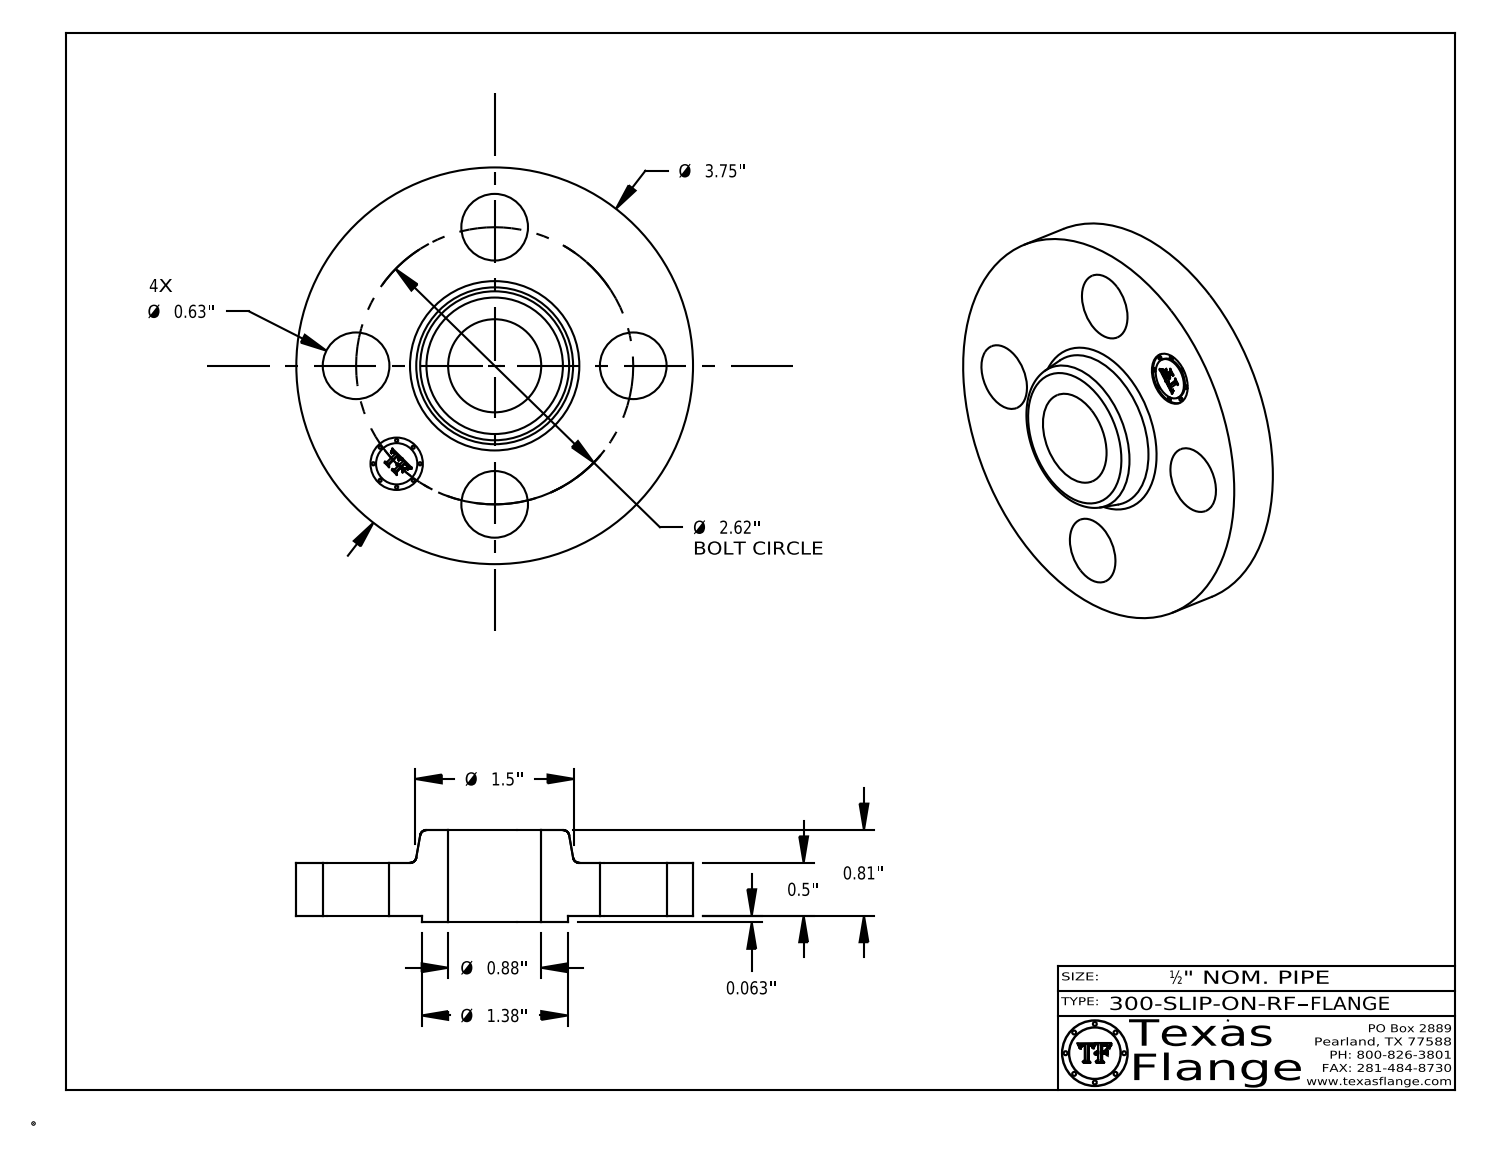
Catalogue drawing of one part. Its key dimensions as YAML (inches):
part_name: "300-SLIP-ON-RF"
step_written_by: "CATIA V5 STEP AP214 (AUTOMOTIVE_DESIGN)"
units: inches
bodies: {solids: 1, faces: 409, planar: 369, cylindrical: 34, other: 6}
overall_size: [3.75, 3.75, 0.873]
volume: 4.97
surface_area: 32.03
round_holes:
  - {diameter: 0.63, count: 4}
  - {diameter: 0.495, count: 1}
  - {diameter: 0.88, count: 1}
round_bosses_or_shafts:
  - {diameter: 0.03, count: 8}
  - {diameter: 3.75, count: 1}
  - {diameter: 1.38, count: 1}
  - {diameter: 0.39, count: 1}
face_to_face_distances: [0.5, 0.063, 0.563, 0.872, 0.81, 0.31, 0.548, 0.485, 0.015, 0.325]
hole_center_spacings: [1.31, 1.852, 1.003, 2.42, 2.62, 1.31]
